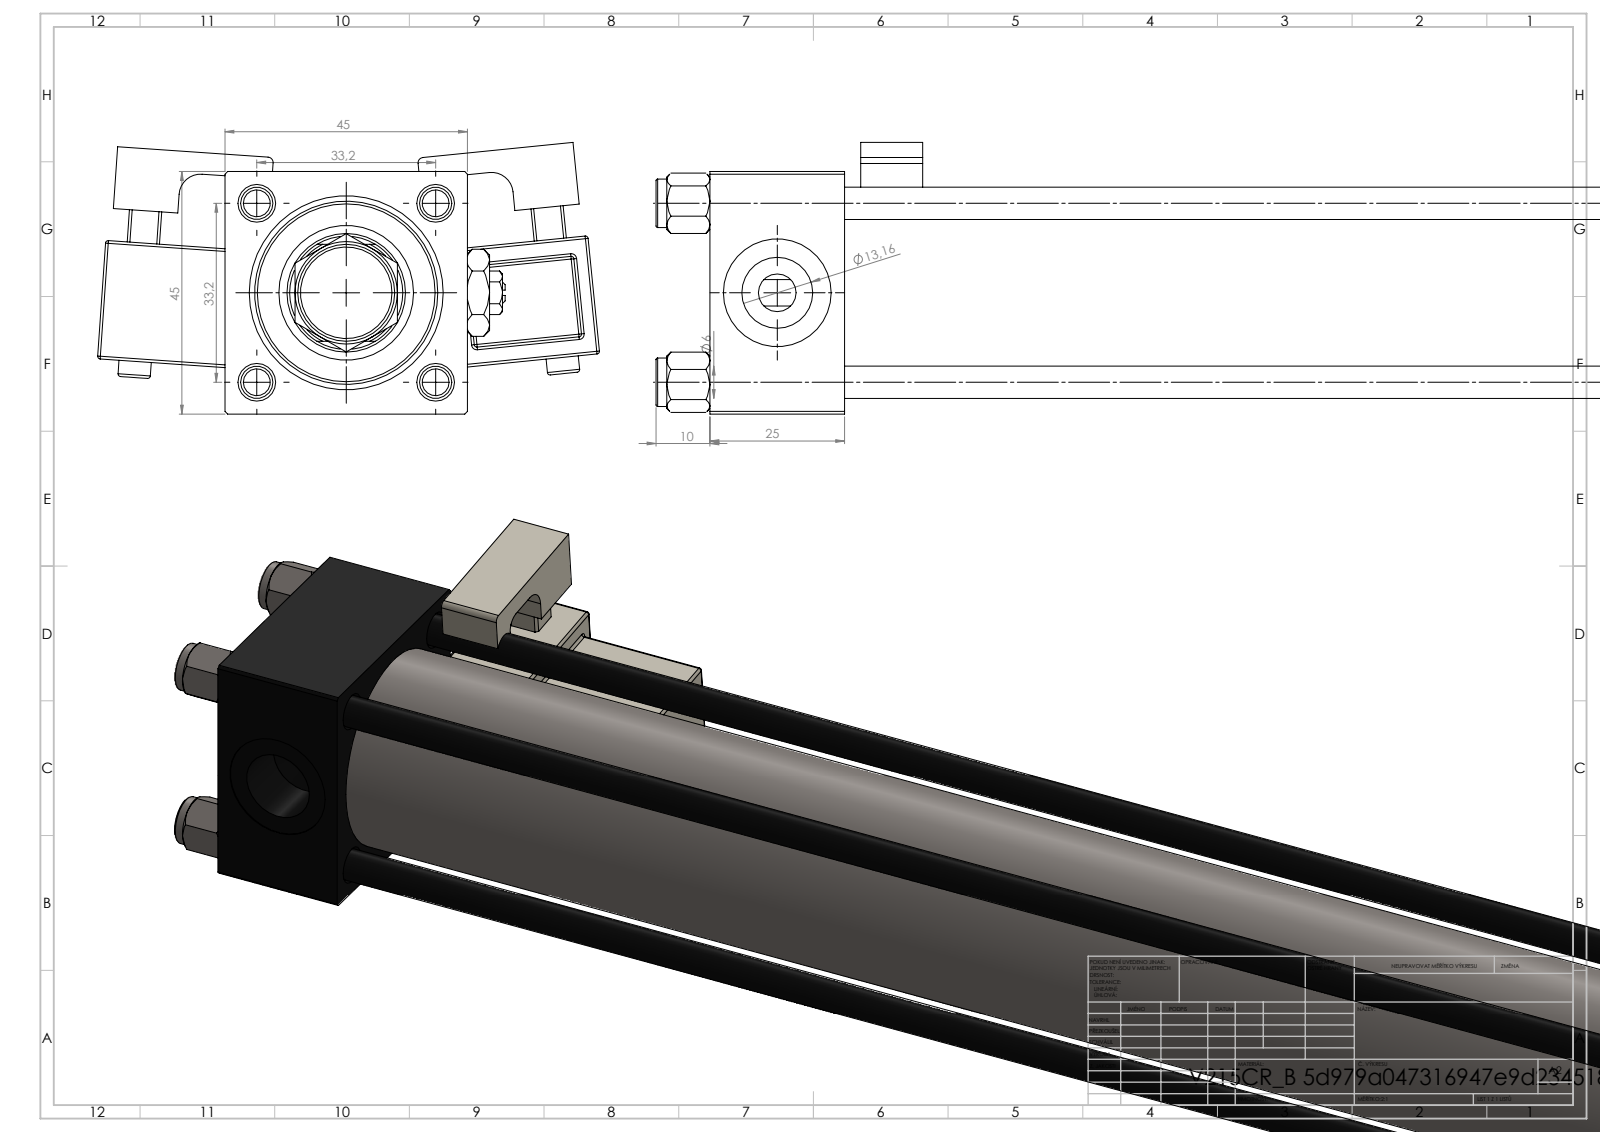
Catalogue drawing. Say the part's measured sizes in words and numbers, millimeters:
The part is named "V215CR_VCP_B; V215_VC_A; V215CR_B_TYCINKA; MFA (+4 more)". Its 3-D file was written by "SolidWorks 2019 (CONFIG_CONTROL_DESIGN)". It is 16 solids with 1466 faces: 556 planar, 152 cylindrical and 758 other. Overall it measures 471 by 93.14 by 50.4 millimeters. Its volume is 491 973 cubic millimeters and its surface area 195 366 square millimeters. Round holes: 4 of diameter 6, 2 of diameter 7, 2 of diameter 13.16, 2 of diameter 20, 1 of diameter 10.5, 1 of diameter 22, 1 of diameter 24, 1 of diameter 25, 1 of diameter 32, 1 of diameter 33. Round bosses or shafts: 4 of diameter 9, 2 of diameter 6, 1 of diameter 38, 1 of diameter 34, 1 of diameter 18, 1 of diameter 11. Partial cylindrical surfaces (rounded edges, fillets, slot ends): 48 of radius 0.5, 2 of radius 1, 2 of radius 2.5, 2 of radius 4, 1 of radius 10.5. The main face-to-face distances are 45, 25, 355, 330, 403, 3, 312.5, 17.5, 44.8, 39.5. The hole center spacings are 23.48, 33.2, 46.95, 355.5.
